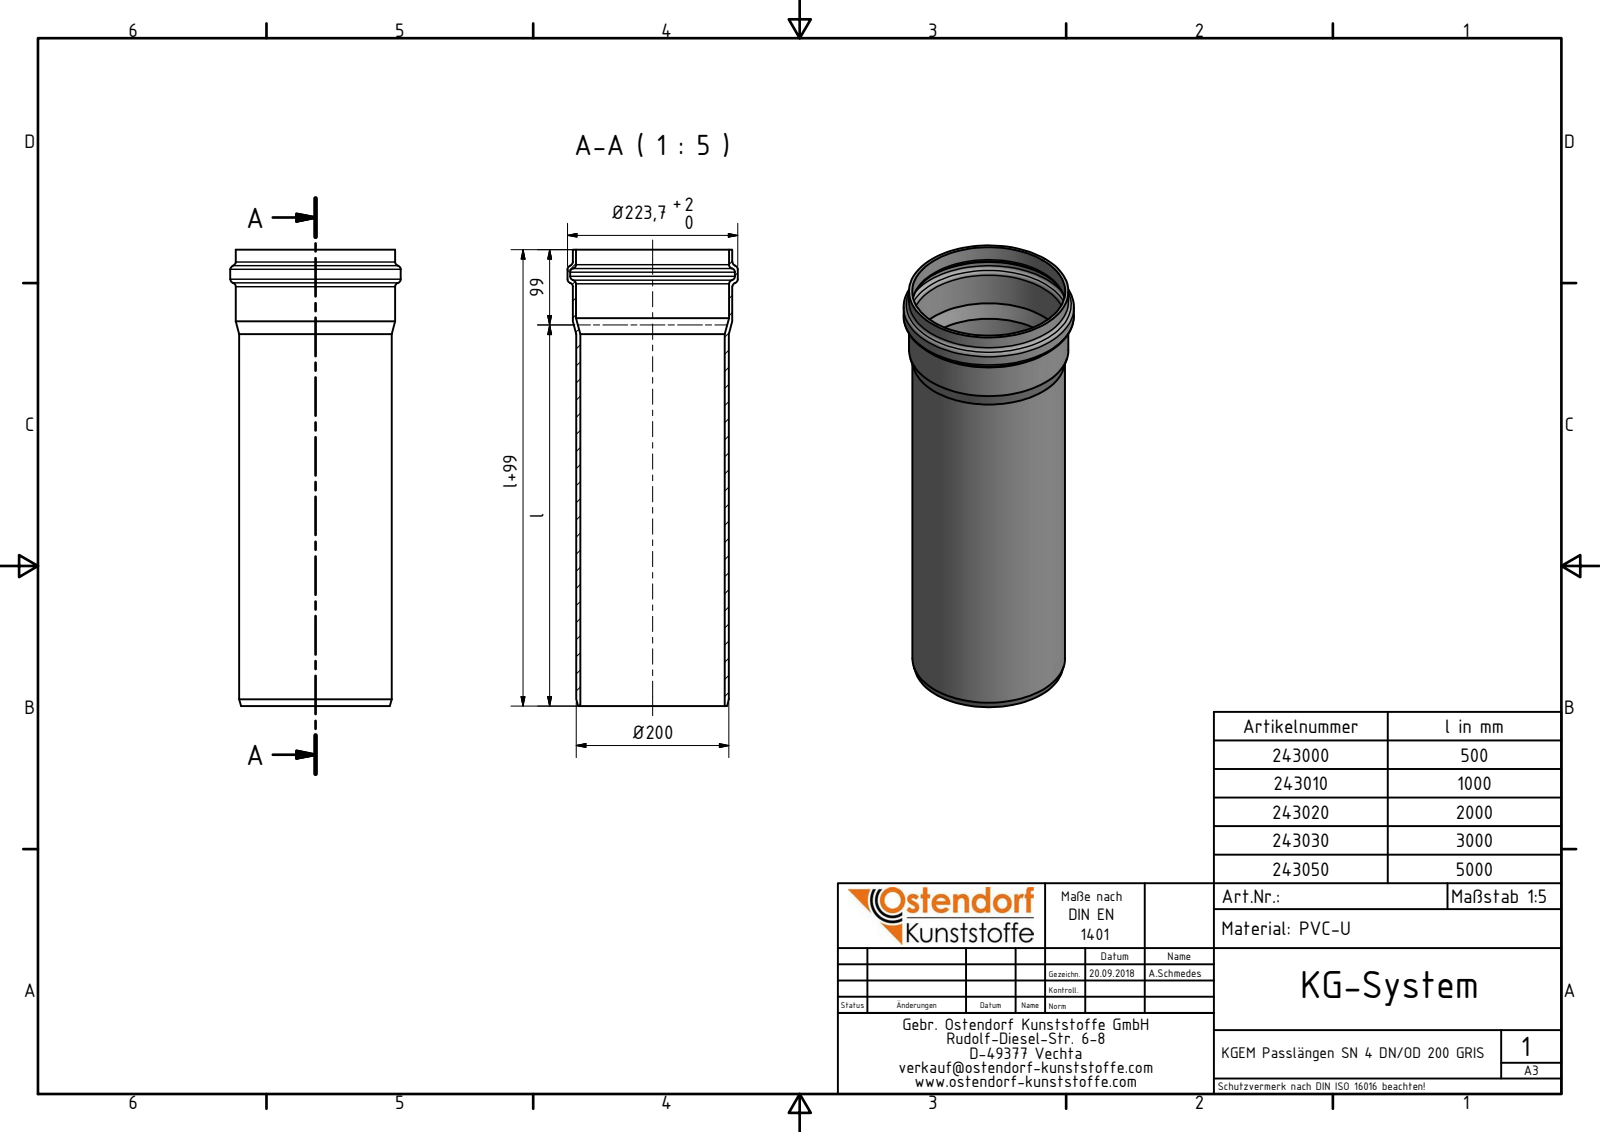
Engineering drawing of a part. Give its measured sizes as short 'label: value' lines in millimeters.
name: 243020 KGEM Passlängen SN 4 DN_OD 200x2000 GRIS
written by: Autodesk Inventor 2016 (AUTOMOTIVE_DESIGN)
unit: mm
bodies: 1 solid, 21 faces (2 planar, 8 cylindrical, 11 other)
size: 2099 × 223.7 × 223.7
volume: 6 792 000 mm³; area: 2 594 000 mm²
holes: 1× ⌀189.65, 1× ⌀200.85, 1× ⌀216.3
bosses: 1× ⌀223.7, 1× ⌀209.25, 1× ⌀200.25
face distances: 2099
